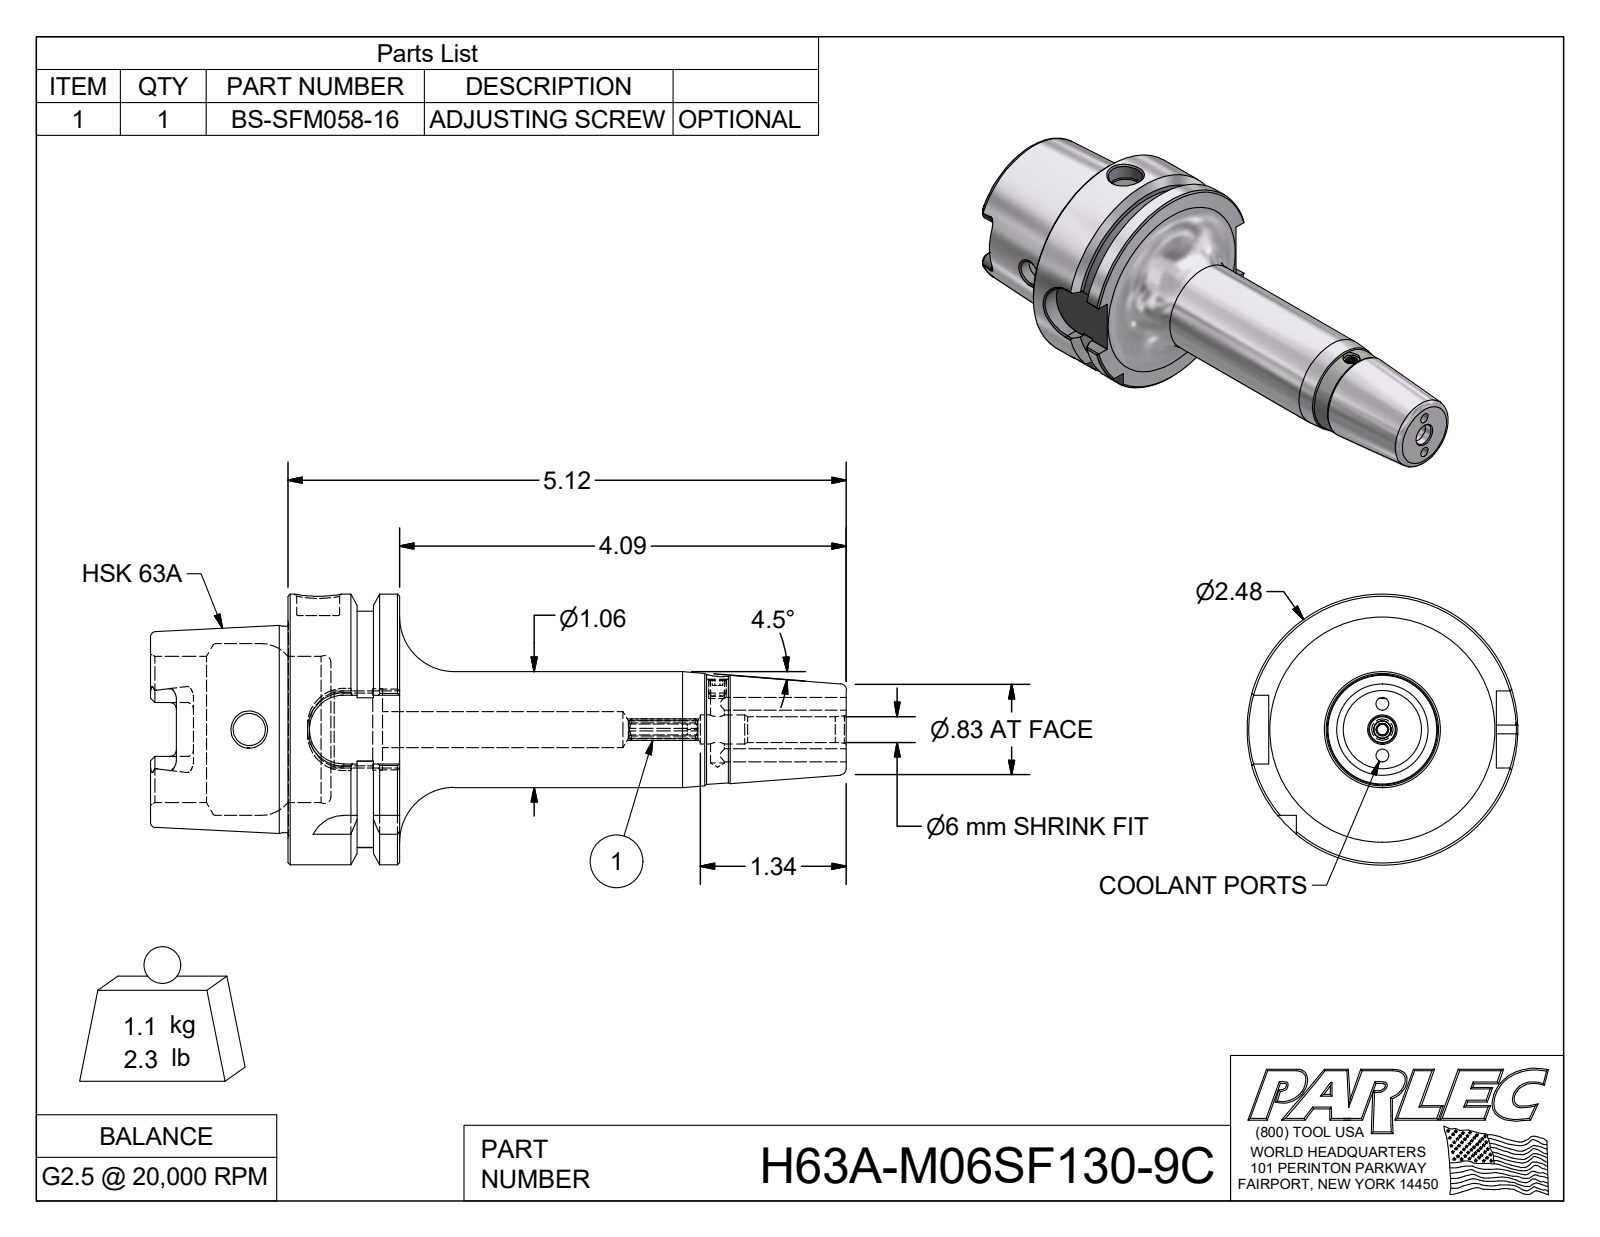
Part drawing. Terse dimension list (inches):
name: H63A-M06SF130-9C; BS-SFM058-16; 029-060
written by: Autodesk Inventor 2018 (AUTOMOTIVE_DESIGN)
unit: in
bodies: 3 solids, 184 faces (72 planar, 46 cylindrical, 66 other)
size: 6.378 × 2.48 × 2.48
volume: 8.244 in³; area: 52.31 in²
holes: 2× ⌀0.118, 1× ⌀0.098, 1× ⌀0.128, 1× ⌀0.163, 1× ⌀0.197, 1× ⌀0.236, 1× ⌀0.266, 1× ⌀0.295, 1× ⌀0.331, 1× ⌀0.394, 1× ⌀0.666, 1× ⌀0.749
bosses: 1× ⌀2.48, 1× ⌀1.891, 1× ⌀1.063, 1× ⌀0.157
rounds: 6× R0.059, 4× R0.113, 4× R0.315, 1× R0.098, 1× R1.083
face distances: 1.024, 0.241, 0.389, 0.394, 0.63, 1.26, 1.654, 2.283, 0.866, 0.157
hole spacings: 0.236, 0.472, 3.661
